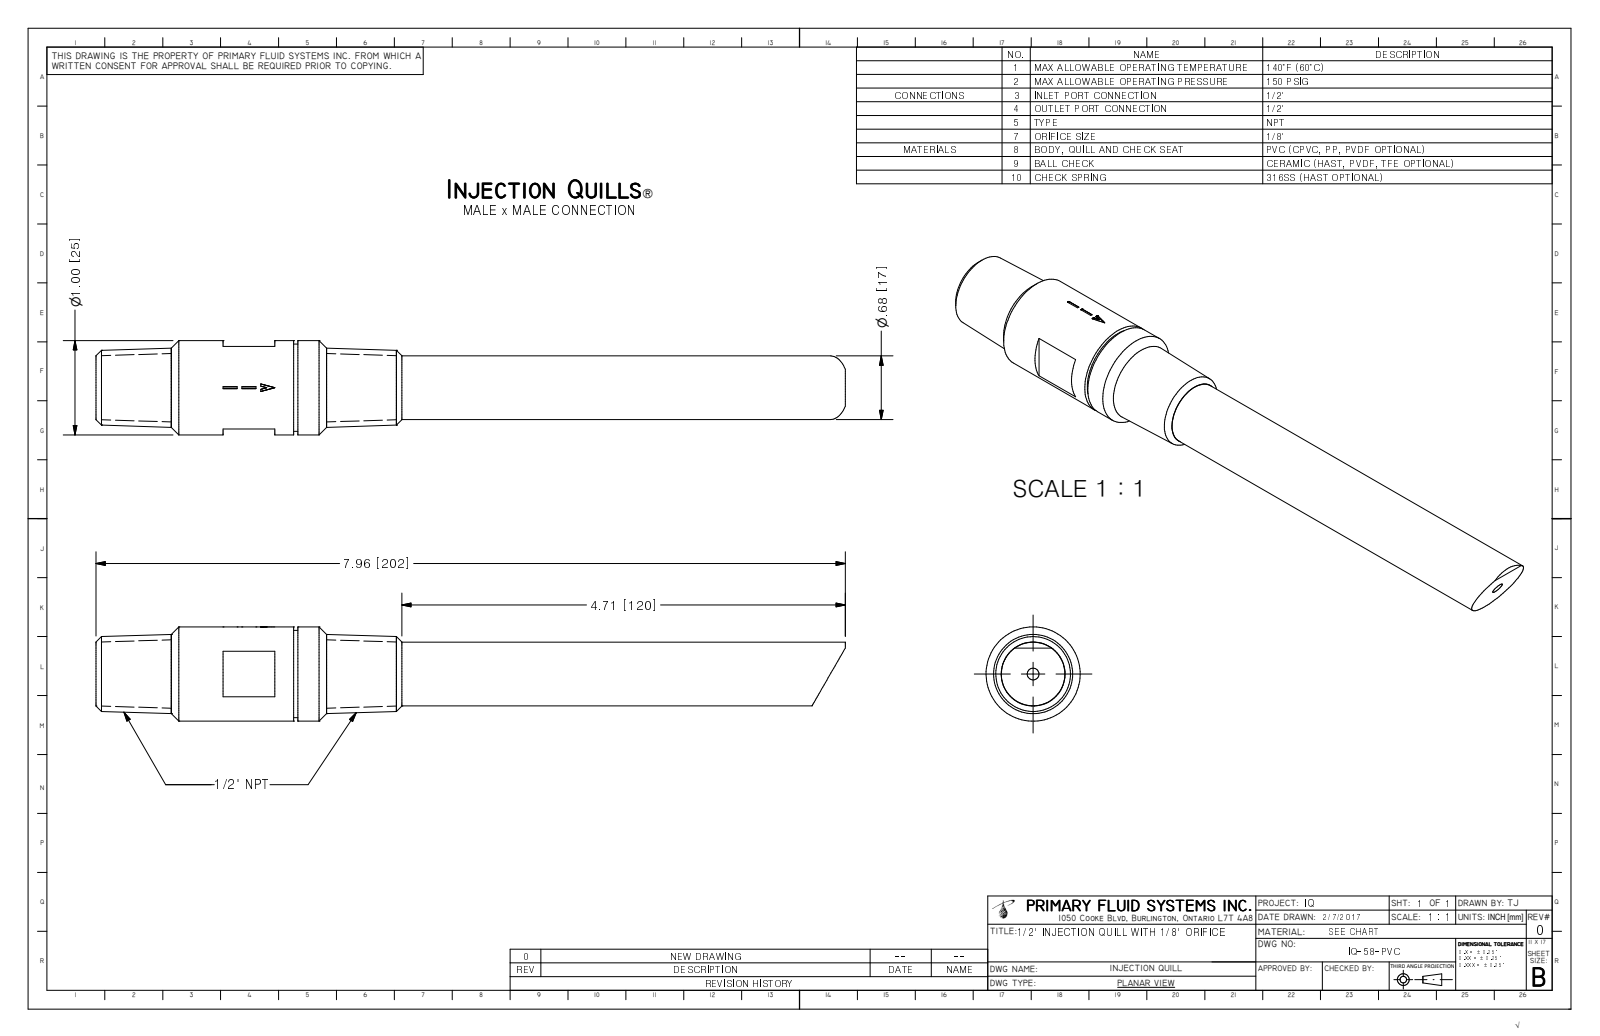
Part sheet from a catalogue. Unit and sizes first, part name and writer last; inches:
Units: inches
Overall size (bounding box): 7.964 × 1 × 1
Round holes (diameter × count): ⌀0.125 ×1, ⌀0.469 ×1, ⌀0.56 ×1
Round bosses / shafts (diameter × count): ⌀1 ×1, ⌀0.925 ×1, ⌀0.675 ×1, ⌀0.558 ×1
Partial cylindrical surfaces — rounded edges, fillets, slot ends (radius × count): R0.499 ×1
Main face-to-face distances: 0.875, 0.75, 1.35, 2.1, 2.145, 1.395, 0.045, 1.9, 1.15, 0.2
Volume: 3.554 in³ · Surface area: 23.81 in²
Bodies: 1 solid, 47 faces (26 planar, 11 cylindrical, 10 other)
Part name (STEP PRODUCT): IQ-58-PVC_R0
STEP written by: Autodesk Inventor 2009 (AUTOMOTIVE_DESIGN)
